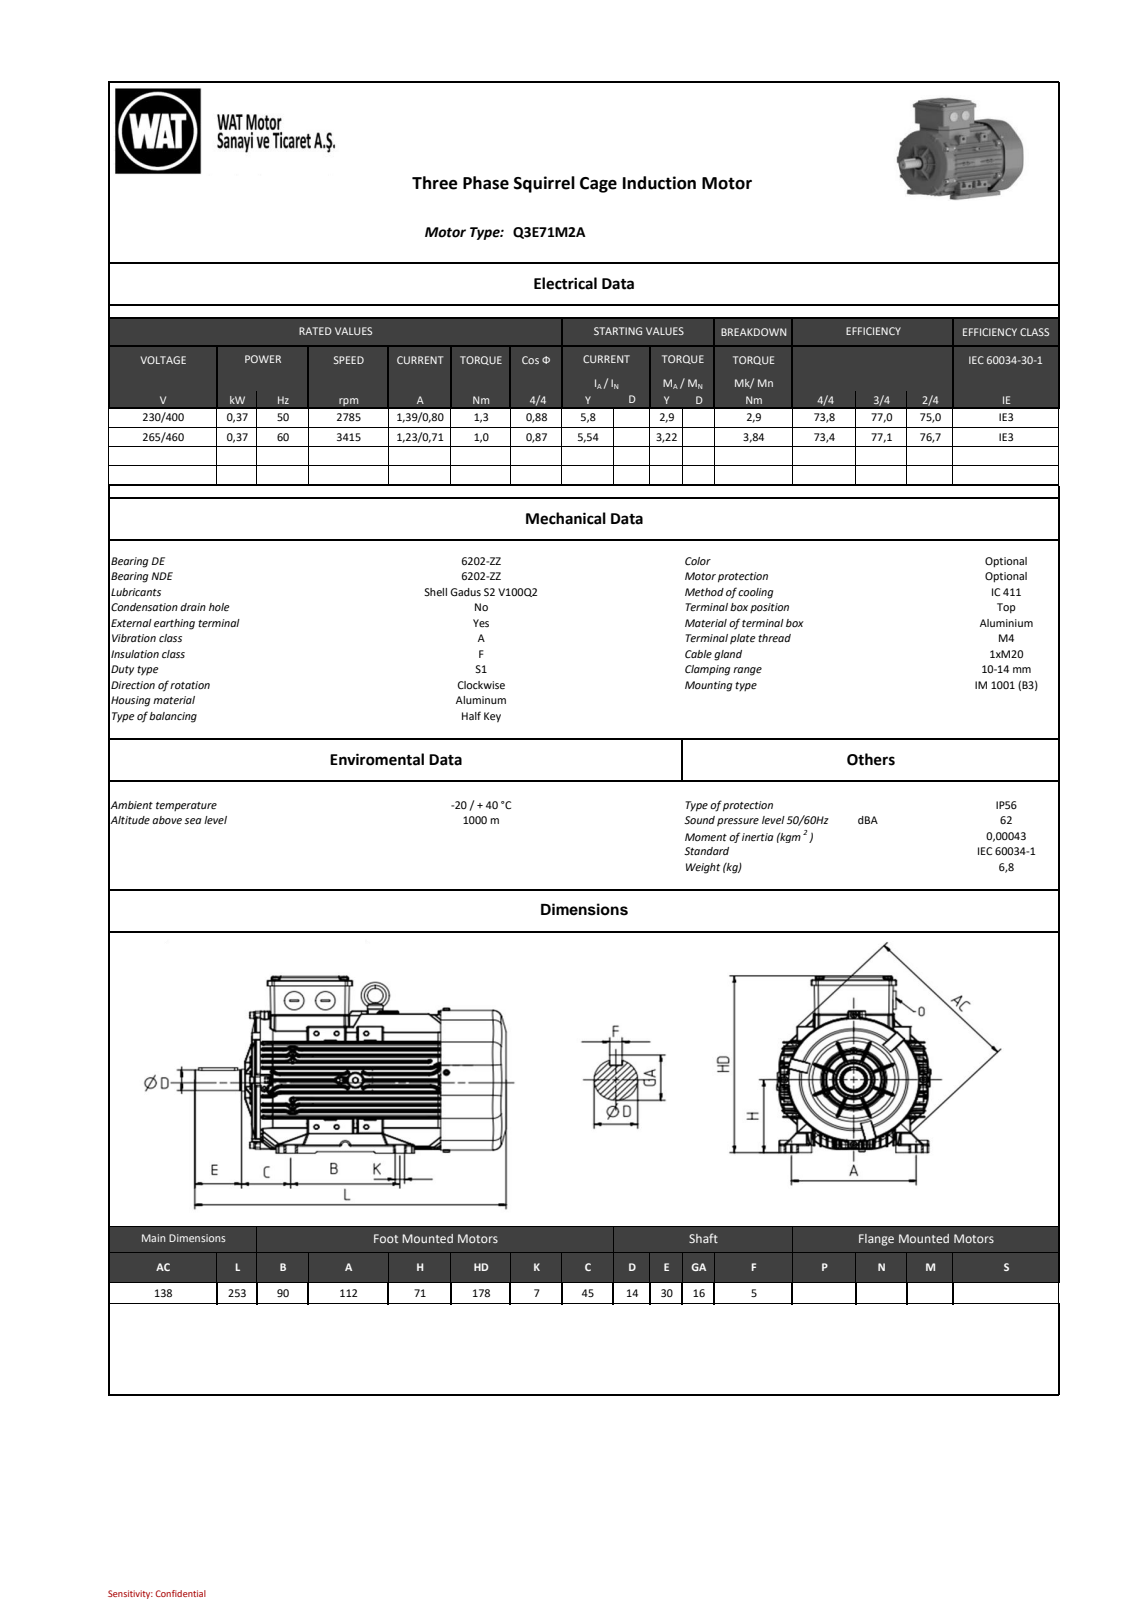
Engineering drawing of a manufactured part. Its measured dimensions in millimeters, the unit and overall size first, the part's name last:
Units: millimetres
Overall size (bounding box): 252 × 178.11 × 138
Round holes (diameter × count): ⌀2.5 ×6, ⌀3.3 ×6, ⌀3.65 ×4, ⌀5.2 ×4, ⌀7 ×4, ⌀3 ×3, ⌀4.8 ×2, ⌀5 ×1, ⌀8 ×1, ⌀14.96 ×1, ⌀18.2 ×1, ⌀19.84 ×1
Round bosses / shafts (diameter × count): ⌀8 ×8, ⌀4 ×6, ⌀138 ×1, ⌀136 ×1, ⌀116 ×1, ⌀115 ×1, ⌀61 ×1, ⌀25.28 ×1
Partial cylindrical surfaces — rounded edges, fillets, slot ends (radius × count): R1 ×84, R1.2 ×36, R1.5 ×20, R0.5 ×18, R0.1 ×9, R0.3 ×8, R4 ×8, R2 ×6
Main face-to-face distances: 15, 5, 172, 24.01, 31.94, 7.93, 177, 1, 4, 7.88
Hole centre spacings: 36.59, 60, 37.26, 61.87, 68.11, 73, 76.74, 87.5
Bodies: 0 solids, 1613 faces (839 planar, 444 cylindrical, 330 other)
Part name (STEP PRODUCT): 001_objects
STEP written by: SIEMENS PLM Software NX2206.8101 (AUTOMOTIVE_DESIGN)
